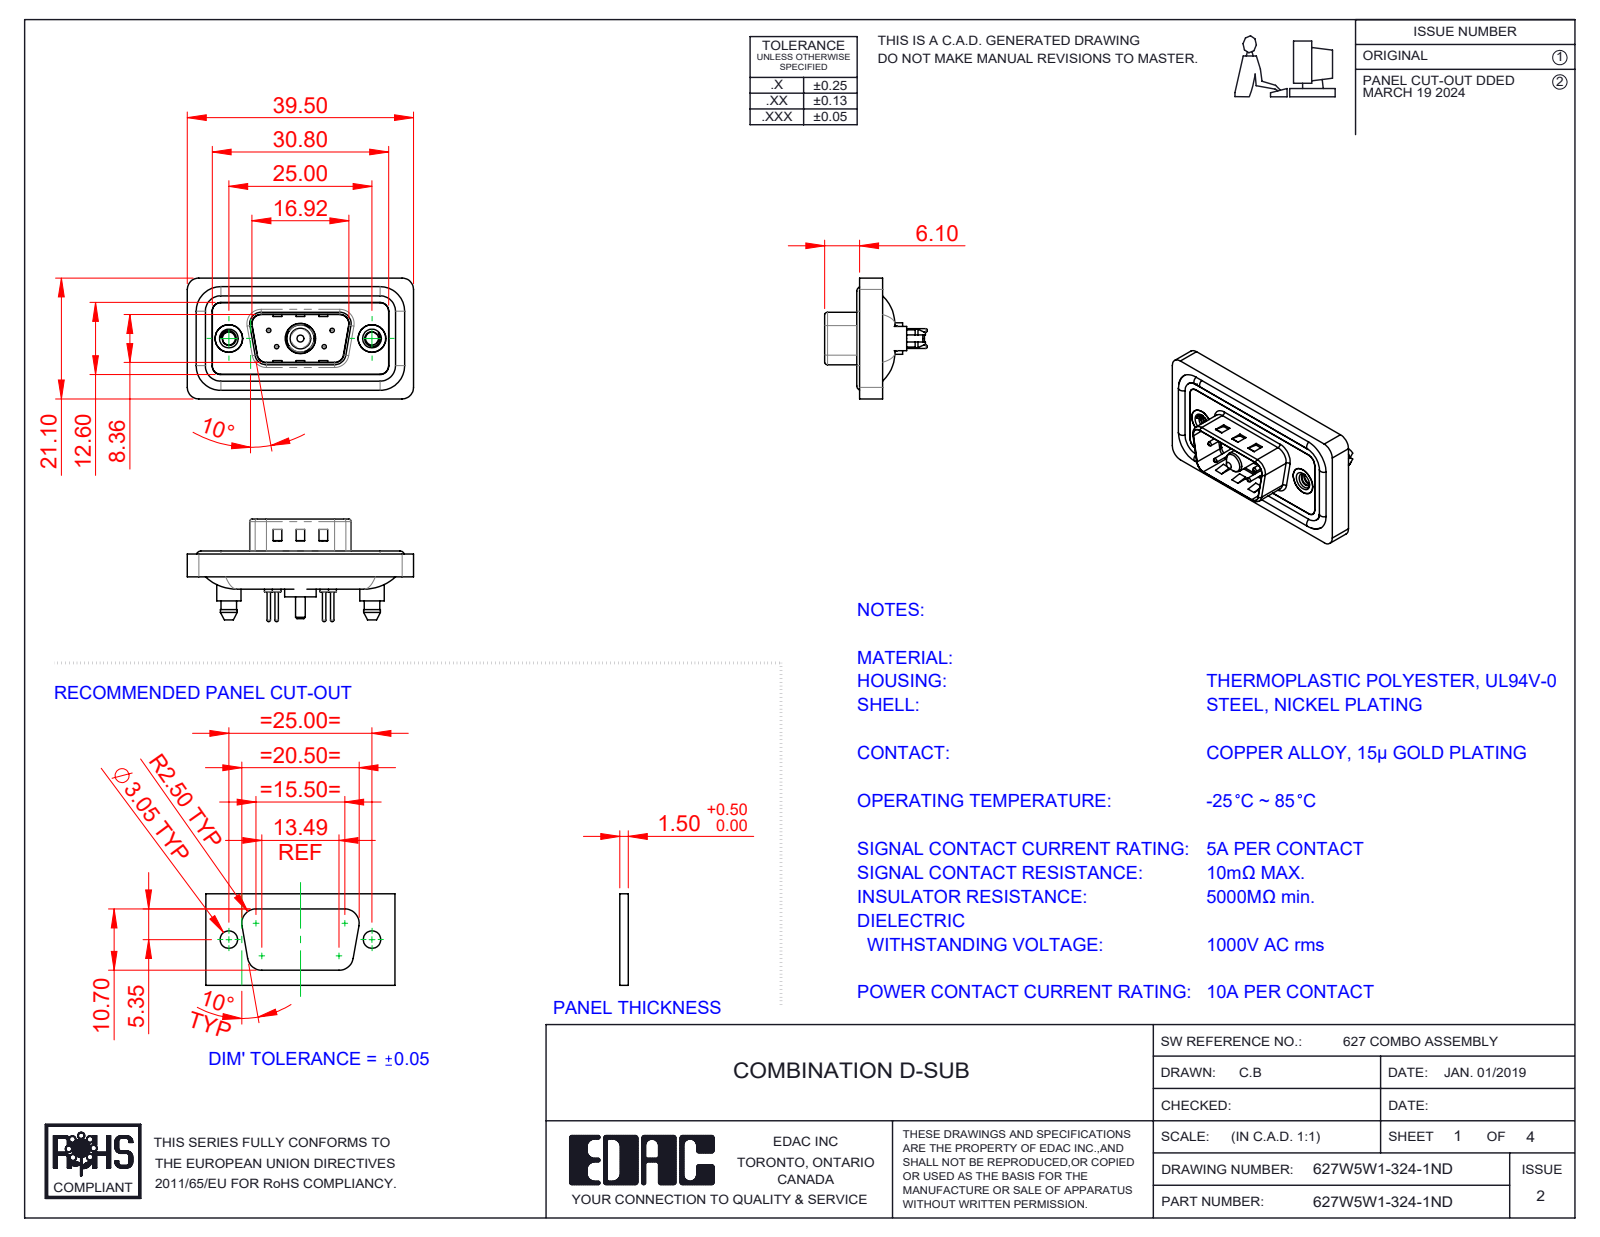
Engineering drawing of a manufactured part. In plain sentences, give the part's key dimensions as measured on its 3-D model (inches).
The part is named "627Combo Threaded Boardlock_D; 627W5W1-324-1ND; 627Combo Housing_5W1; 627Combo Contact Row 1_24 (+6 more)". Its 3-D file was written by "SolidWorks 2023 (CONFIG_CONTROL_DESIGN)". It is 13 solids with 656 faces: 199 planar, 295 cylindrical and 162 other. Overall it measures 1.555 by 0.831 by 0.705 inches. Its volume is 0.275 cubic inches and its surface area 11.26 square inches. Round holes: 4 of diameter 0.03, 4 of diameter 0.063, 4 of diameter 0.079, 2 of diameter 0.089, 2 of diameter 0.157, 2 of diameter 0.189, 2 of diameter 0.197, 1 of diameter 0.191, 1 of diameter 0.209. Round bosses or shafts: 4 of diameter 0.063, 4 of diameter 0.059, 4 of diameter 0.024, 2 of diameter 0.213, 2 of diameter 0.193, 2 of diameter 0.167, 1 of diameter 0.217, 1 of diameter 0.205. Partial cylindrical surfaces (rounded edges, fillets, slot ends): 24 of radius 0.059, 18 of radius 0.079, 10 of radius 0.063, 8 of radius 0.02, 4 of radius 0.01, 4 of radius 0.024, 4 of radius 0.026, 4 of radius 0.035. The main face-to-face distances are 0.016, 0.043, 0.114, 0.063, 0.059, 0.122, 0.02, 0.098, 0.157, 0.028. The hole center spacings are 0.124, 0.225, 0.28, 0.492, 0.713, 0.173, 0.173, 0.327.
